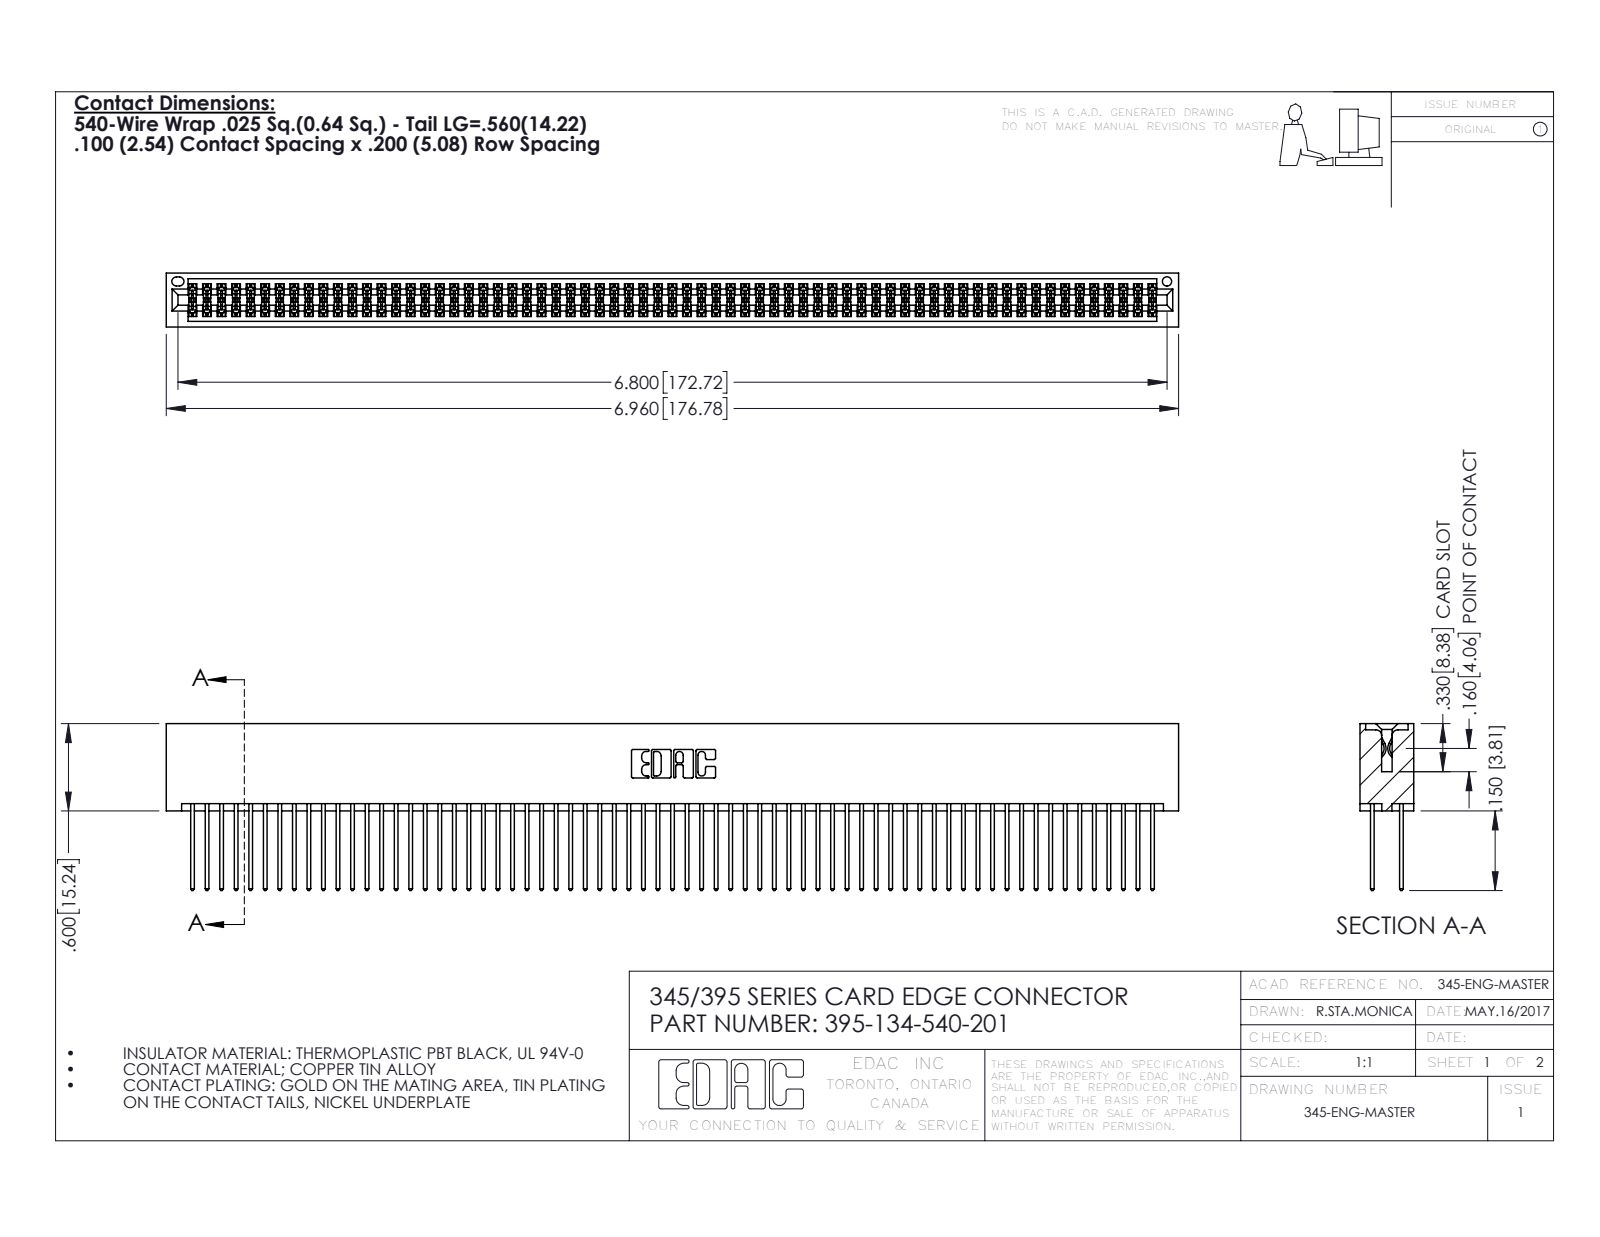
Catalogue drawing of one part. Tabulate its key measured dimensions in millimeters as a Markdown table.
| quantity | value |
| --- | --- |
| part name | 345 Part_No Mounting Lugs; 345-292-001_345-293-140; 395-134-540-201 |
| STEP written by | SolidWorks 2016 (CONFIG_CONTROL_DESIGN) |
| units | millimeters |
| bodies | 135 solids, 6818 faces (4498 planar, 2320 cylindrical, 0 other) |
| overall size | 176.8 × 29.1 × 9.4 |
| volume | 18 530 mm³ |
| surface area | 30 540 mm² |
| round holes (diameter × count) | 1.6 × 1 |
| partial cylindrical surfaces (radius × count) | 0.2 × 201, 0.3 × 134, 0.3 × 22, 0.2 × 6, 0.8 × 6, 0.7 × 3, 0.4 × 2, 0.5 × 2 |
| main face-to-face distances | 7.6, 1.8, 5.1, 2.5, 6.9, 0.6, 5.7, 9.4, 4.4, 3.8 |
